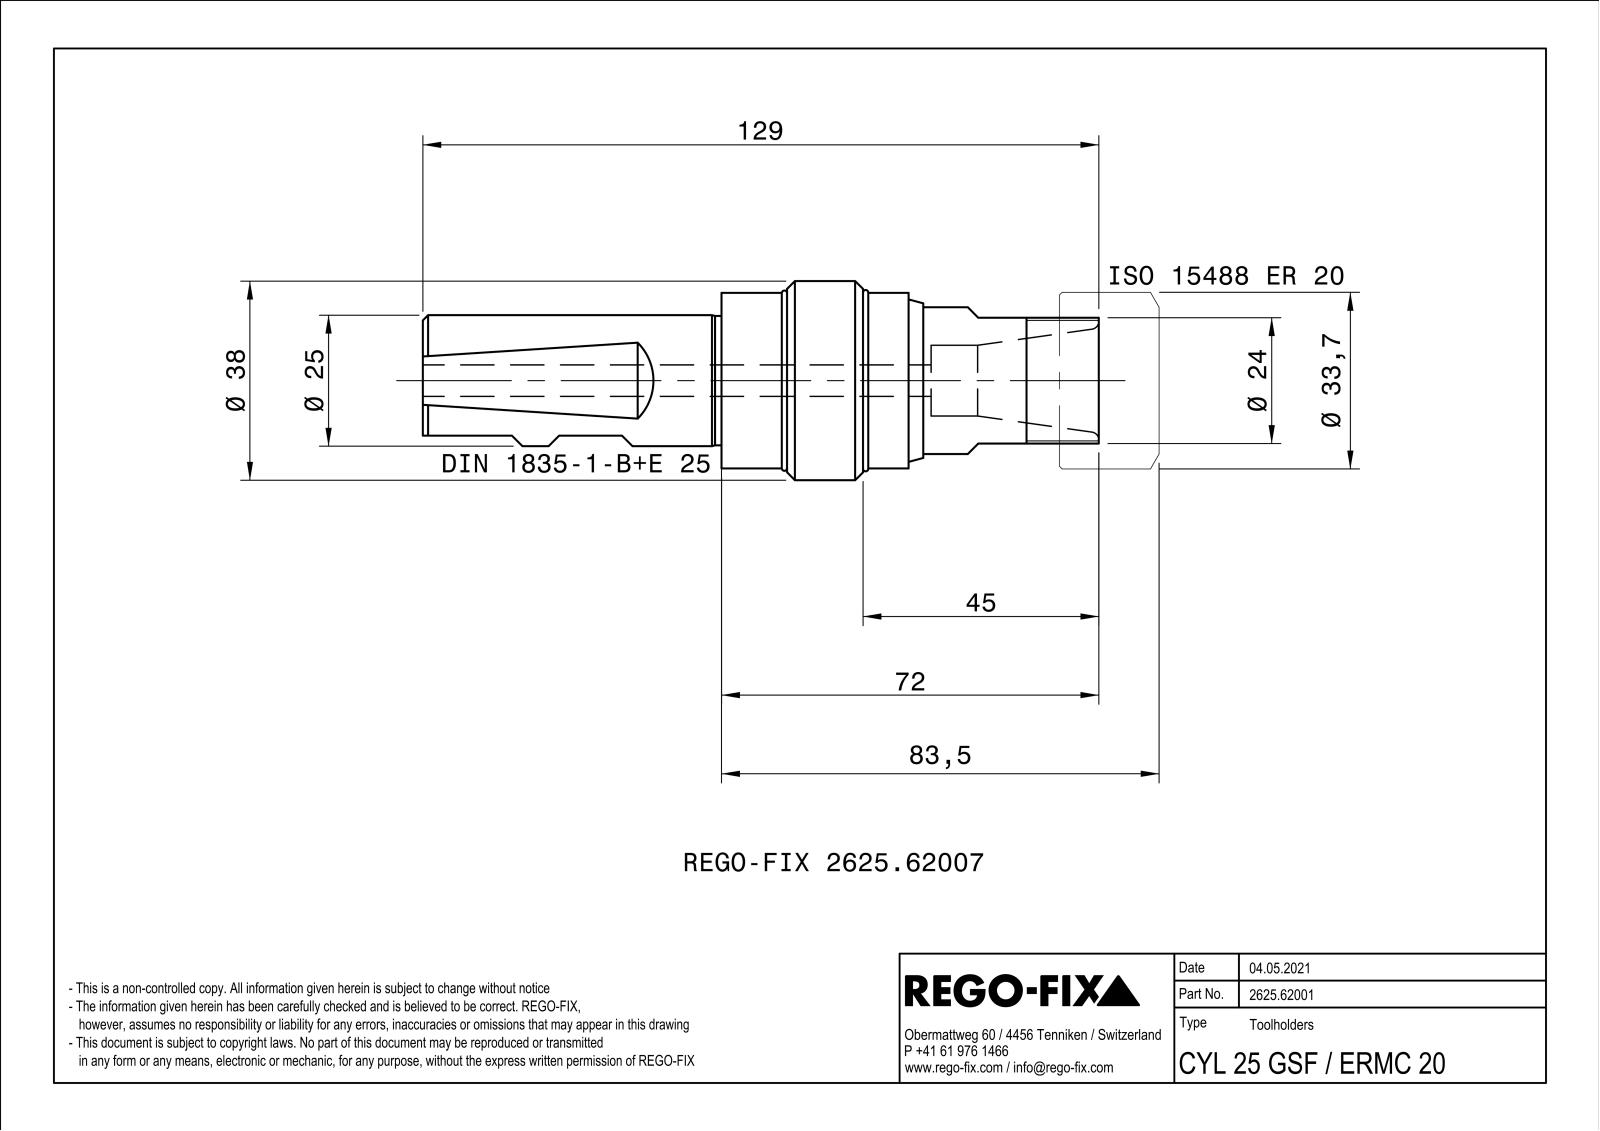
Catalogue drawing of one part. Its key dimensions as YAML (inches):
part_name: "NOCUT"
step_written_by: "SIEMENS PLM Software Solid Edge ST10 (AUTOMOTIVE_DESIGN)"
units: inches
bodies: {solids: 1, faces: 61, planar: 33, cylindrical: 15, other: 13}
overall_size: [5.079, 1.496, 1.496]
volume: 4.475
surface_area: 25.28
round_holes:
  - {diameter: 0.098, count: 1}
  - {diameter: 0.236, count: 1}
  - {diameter: 0.531, count: 1}
round_bosses_or_shafts:
  - {diameter: 1.496, count: 1}
  - {diameter: 1.319, count: 1}
  - {diameter: 1.22, count: 1}
  - {diameter: 1.102, count: 1}
  - {diameter: 0.984, count: 1}
  - {diameter: 0.945, count: 1}
  - {diameter: 0.882, count: 1}
  - {diameter: 0.492, count: 1}
partial_cylinders:
  - {radius: 0.063, count: 1}
face_to_face_distances: [2.244, 2.165, 4.409, 0.512, 0.76, 1.406, 3.65, 0.248, 1.654, 3.898]
